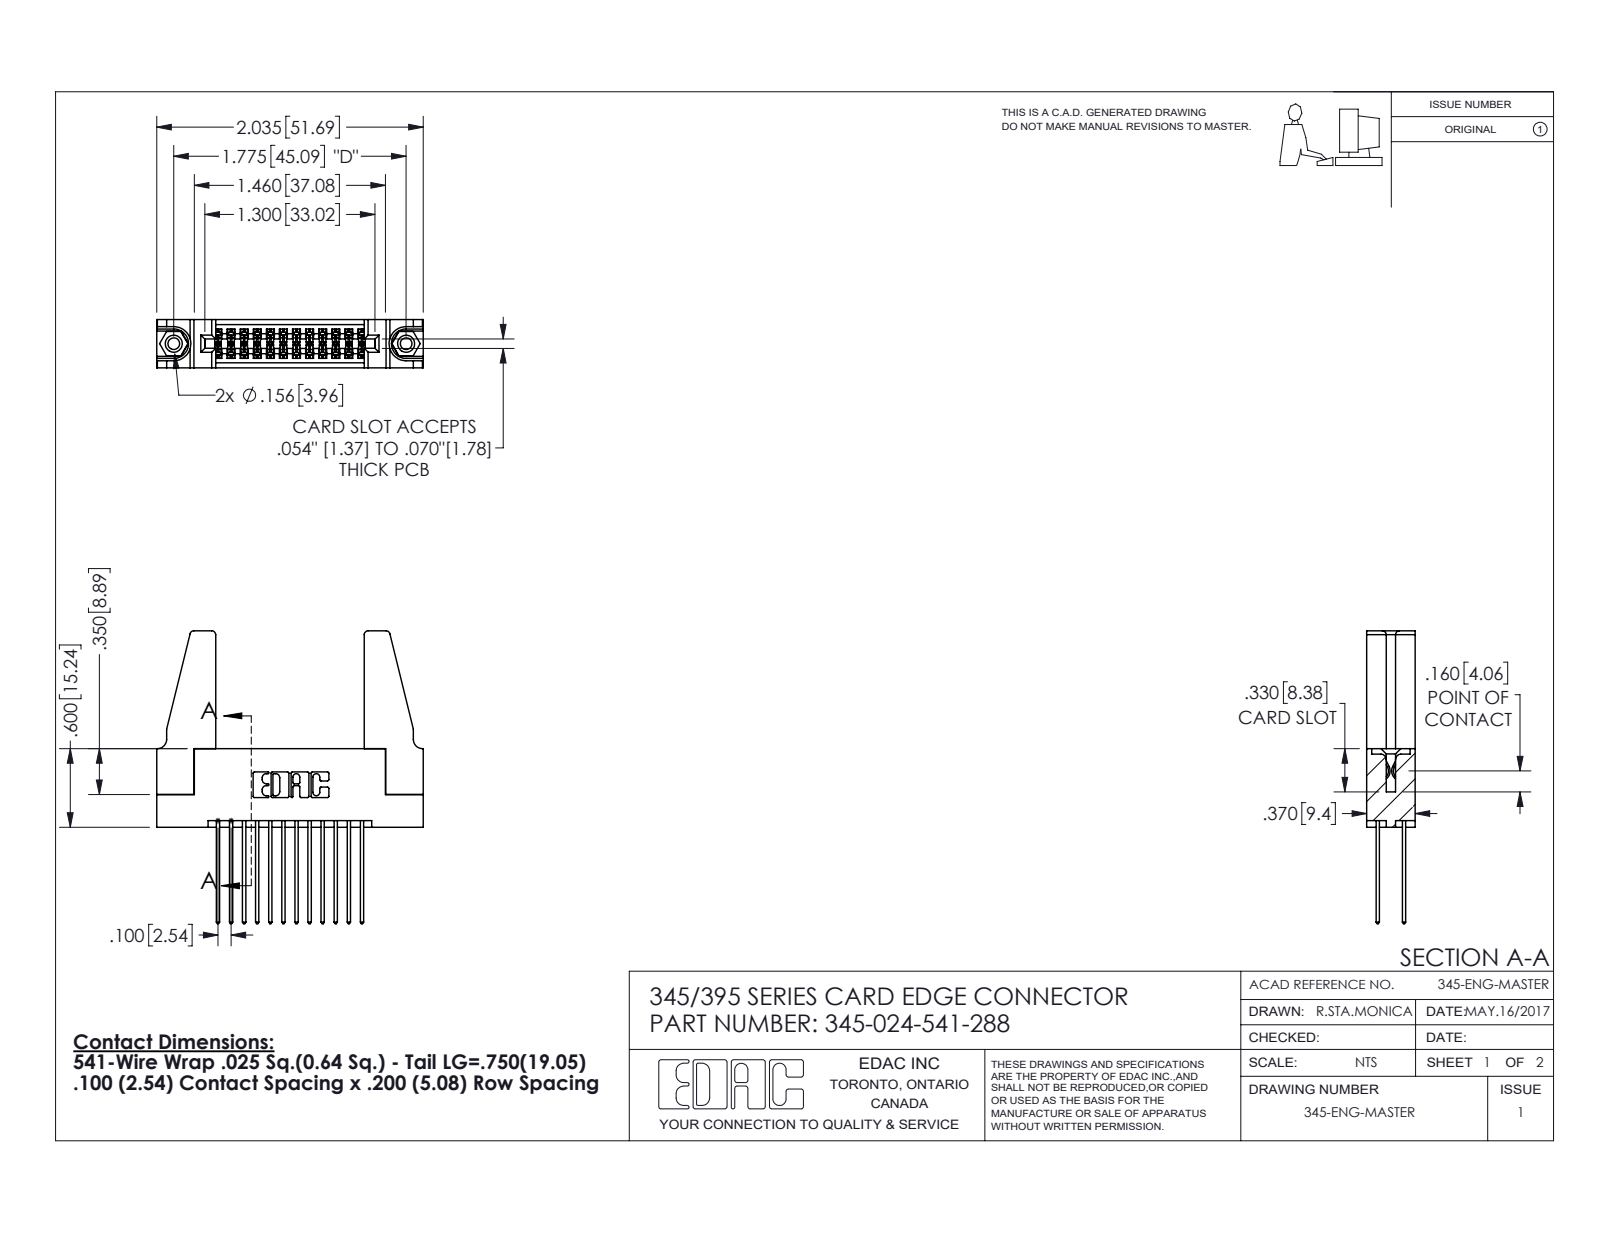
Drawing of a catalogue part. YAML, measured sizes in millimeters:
part_name: "345-220-078_345-220-088; 345 Part_Flush Mounting Lugs - 0.156 Dia-TH; 345-250-001_345-250-001-102; 345-292-001_345-293-141 (+1 more)"
step_written_by: "SolidWorks 2016 (CONFIG_CONTROL_DESIGN)"
units: millimeters
bodies: {solids: 29, faces: 1450, planar: 944, cylindrical: 490, other: 16}
overall_size: [56.8, 51.7, 9.4]
volume: 8130
surface_area: 10410
round_holes:
  - {diameter: 2.3, count: 2}
  - {diameter: 3.2, count: 2}
  - {diameter: 4, count: 2}
  - {diameter: 1.6, count: 1}
round_bosses_or_shafts:
  - {diameter: 3.9, count: 2}
partial_cylinders:
  - {radius: 0.2, count: 36}
  - {radius: 0.3, count: 24}
  - {radius: 0.3, count: 22}
  - {radius: 0.8, count: 8}
  - {radius: 0.2, count: 6}
  - {radius: 0.8, count: 6}
  - {radius: 0.7, count: 3}
  - {radius: 0.4, count: 2}
face_to_face_distances: [1.8, 7.6, 9.4, 5.1, 2.5, 6.9, 0.6, 5.7, 4.4, 3.8]
hole_center_spacings: [6.9, 39.2, 45.1]
